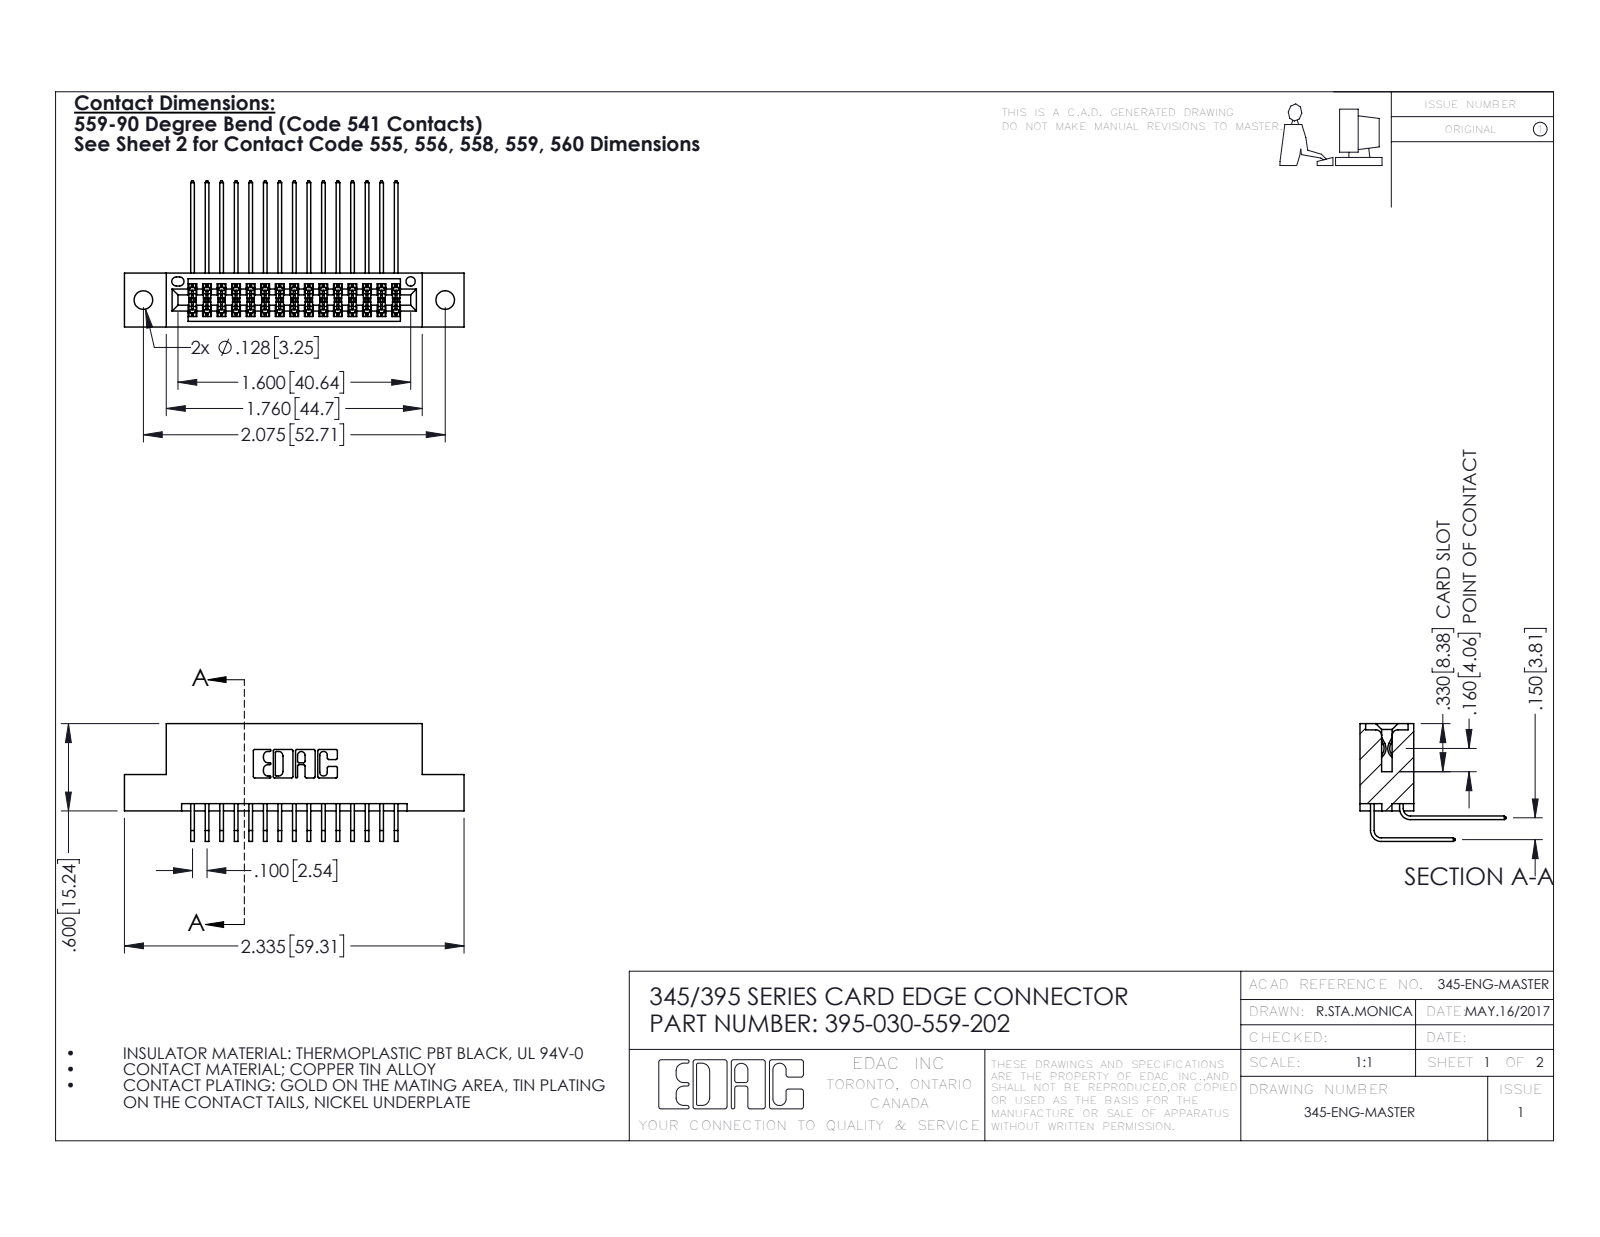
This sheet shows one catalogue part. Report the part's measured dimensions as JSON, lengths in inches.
{"part_name": "345 Part_Flush Mounting Lugs - 0.128 Dia; 345-292-001_558 559 Tail - 1; 345-292-001_559 Tail - 2; 395-030-559-202", "step_written_by": "SolidWorks 2016 (CONFIG_CONTROL_DESIGN)", "units": "inches", "bodies": {"solids": 31, "faces": 1686, "planar": 1130, "cylindrical": 556, "other": 0}, "overall_size": [2.335, 1.005, 0.809], "volume_in3": 0.345, "surface_area_in2": 12.97, "round_holes": [[0.128, 2], [0.064, 1]], "partial_cylinders_radius": [[0.006, 46], [0.01, 22], [0.007, 6], [0.031, 6], [0.026, 3], [0.014, 2], [0.019, 2], [0.022, 2]], "face_to_face_distances": [0.072, 0.298, 0.2, 0.37, 0.098, 0.272, 0.025, 0.225, 0.15, 0.175], "hole_center_spacings": [0.27, 1.842, 2.075]}
